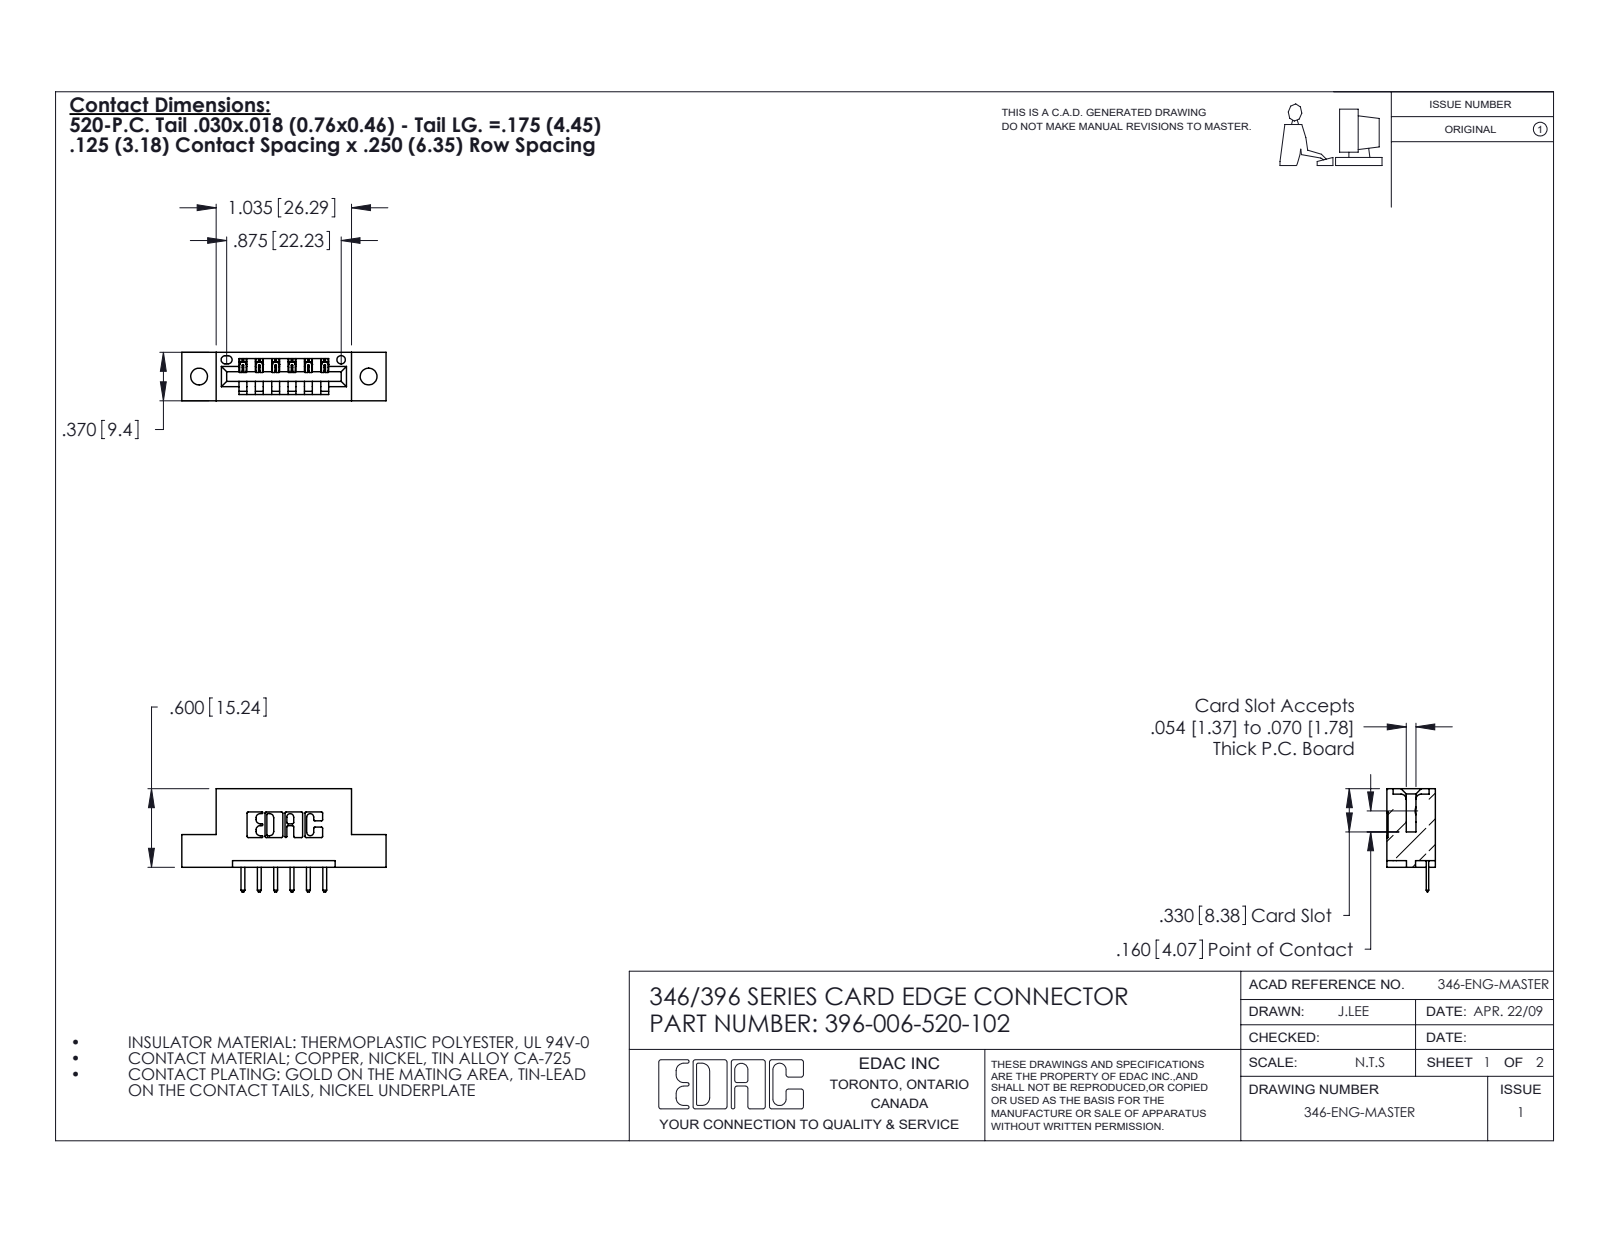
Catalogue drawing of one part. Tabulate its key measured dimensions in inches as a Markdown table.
| quantity | value |
| --- | --- |
| part name | 345-292-001_345-293-120; 396-006-520-102; 346 Part_Flush Mounting Lugs - 0.128 Dia |
| STEP written by | SolidWorks 2020 (CONFIG_CONTROL_DESIGN) |
| units | inches |
| bodies | 7 solids, 494 faces (328 planar, 166 cylindrical, 0 other) |
| overall size | 1.56 × 0.788 × 0.37 |
| volume | 0.213 in³ |
| surface area | 5.651 in² |
| round holes (diameter × count) | 0.128 × 2, 0.064 × 1 |
| partial cylindrical surfaces (radius × count) | 0.01 × 22, 0.01 × 14, 0.006 × 12, 0.007 × 6, 0.031 × 6, 0.026 × 3, 0.031 × 2, 0.04 × 2 |
| main face-to-face distances | 0.25, 0.37, 0.048, 0.322, 0.148, 0.222, 0.1, 0.174, 0.125, 0.125 |
| hole center spacings | 0.246, 1.092, 1.295 |
